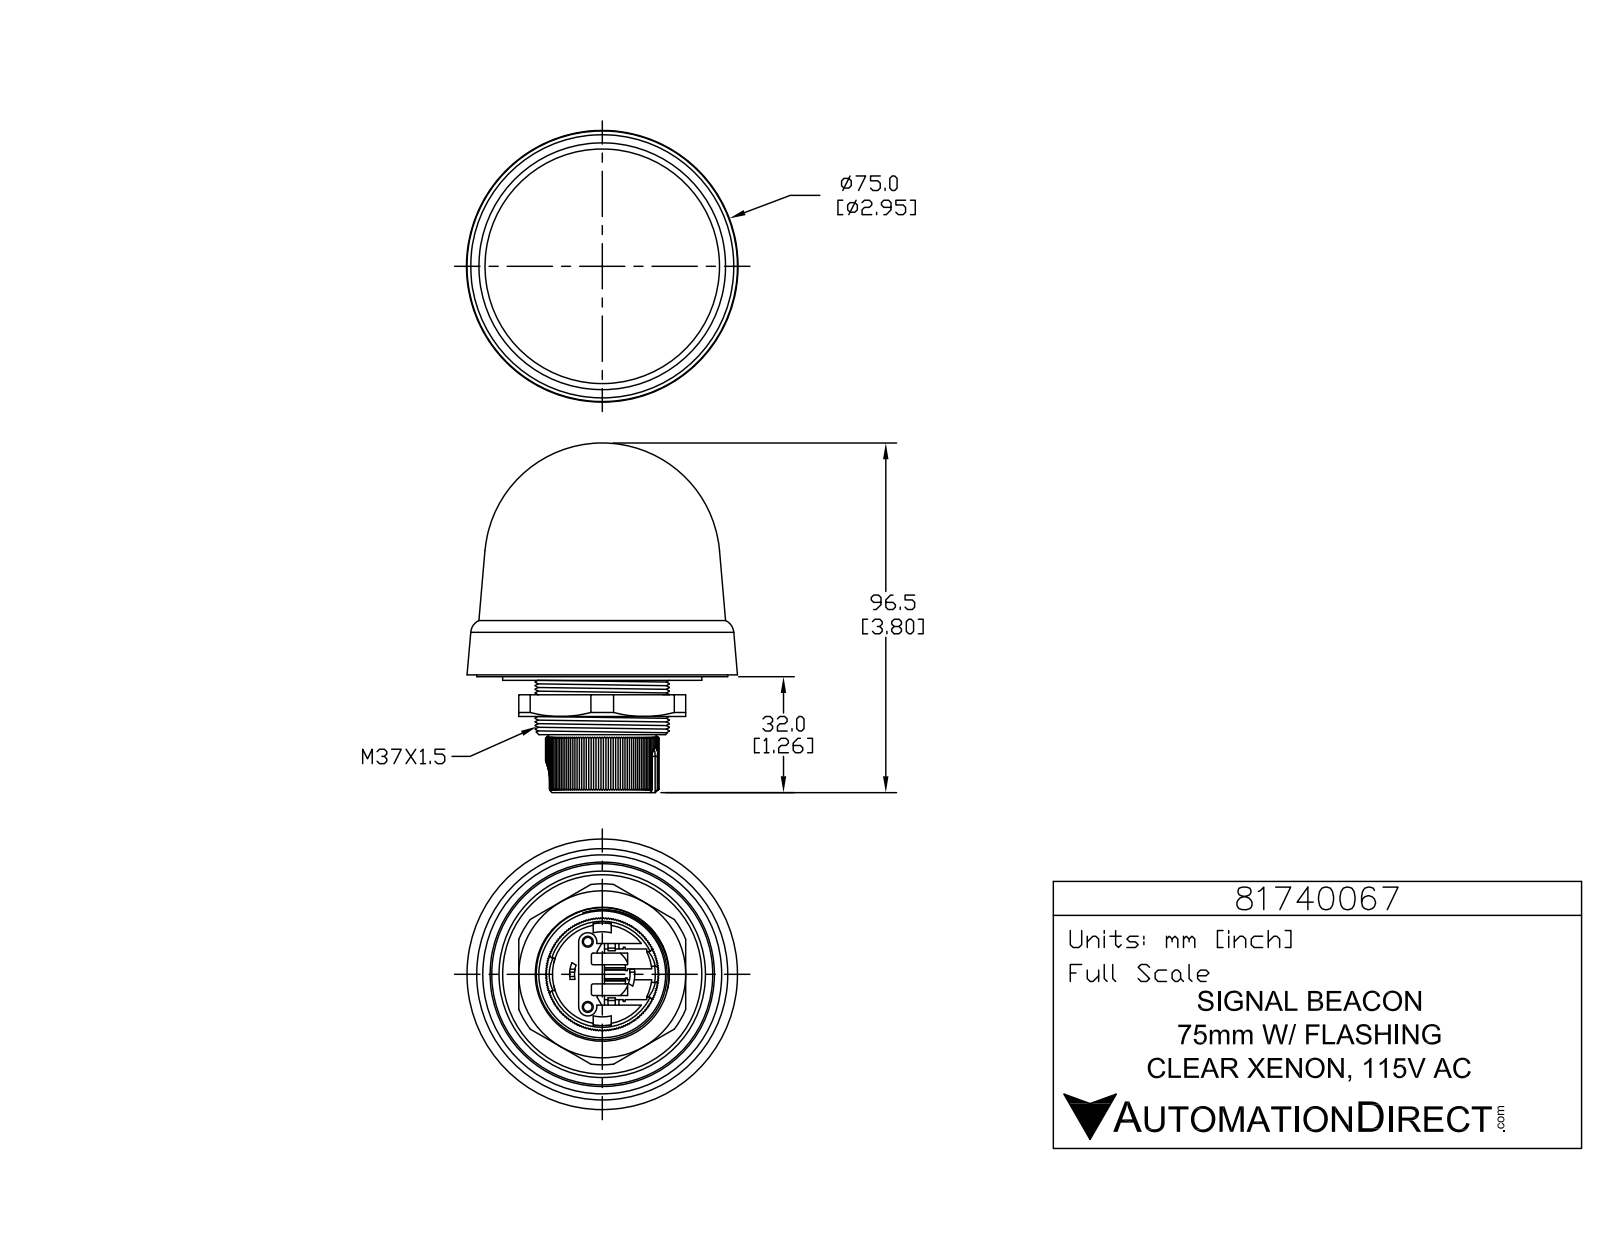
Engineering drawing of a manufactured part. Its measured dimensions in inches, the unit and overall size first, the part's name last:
Units: inches
Overall size (bounding box): 3.799 × 2.941 × 2.941
Round holes (diameter × count): ⌀0.094 ×2, ⌀0.118 ×2, ⌀0.604 ×1, ⌀1.142 ×1
Round bosses / shafts (diameter × count): ⌀0.217 ×2, ⌀0.067 ×2, ⌀2.165 ×1, ⌀1.457 ×1, ⌀0.925 ×1
Partial cylindrical surfaces — rounded edges, fillets, slot ends (radius × count): R0.008 ×6, R0.039 ×6, R0.02 ×4, R0.031 ×2, R0.079 ×2, R0.098 ×2, R0.177 ×1, R0.354 ×1
Main face-to-face distances: 0.177, 0.354, 0.197, 0.433, 0.512, 0.335, 0.059, 0.394, 0.118, 0.157
Hole centre spacings: 0.388, 0.709
Volume: 12.36 in³ · Surface area: 58.68 in²
Bodies: 3 solids, 560 faces (432 planar, 80 cylindrical, 48 other)
Part name (STEP PRODUCT): 81740067
STEP written by: SolidWorks 2019 (CONFIG_CONTROL_DESIGN)
